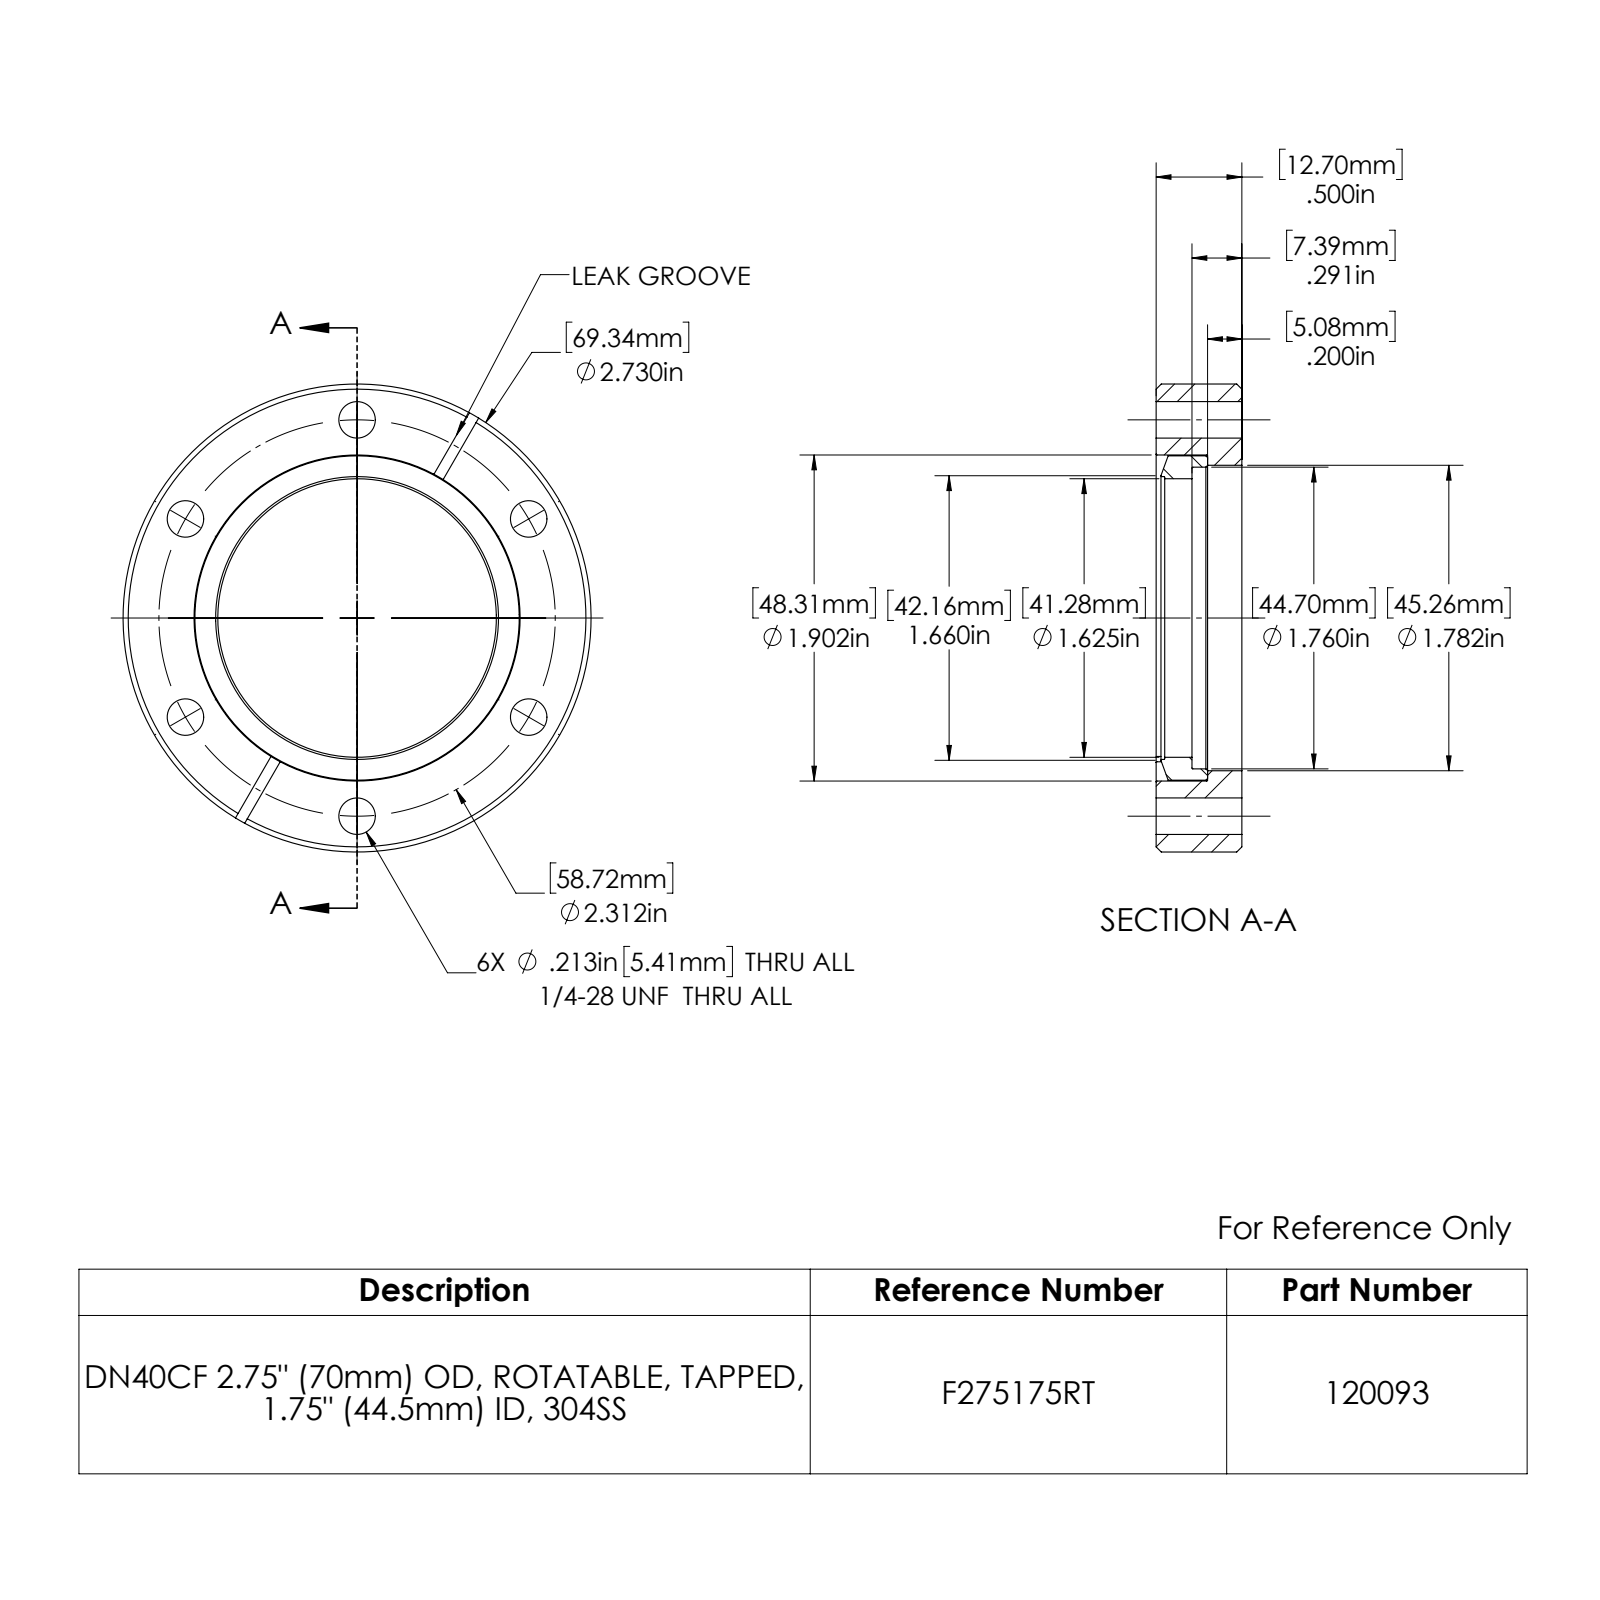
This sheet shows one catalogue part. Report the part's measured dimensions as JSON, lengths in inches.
{"part_name": "990367; 990365; 120093_A", "step_written_by": "SolidWorks 2022 (CONFIG_CONTROL_DESIGN)", "units": "inches", "bodies": {"solids": 2, "faces": 61, "planar": 13, "cylindrical": 26, "other": 22}, "overall_size": [2.73, 2.73, 0.5], "volume_in3": 1.61, "surface_area_in2": 19.47, "round_holes": [[0.213, 6], [1.625, 1], [1.65, 1], [1.76, 1], [1.782, 1], [1.902, 1]], "round_bosses_or_shafts": [[2.73, 1], [1.892, 1]], "face_to_face_distances": [0.5, 0.3, 0.2, 0.209, 0.091, 0.291, 0.062, 0.147, 0.238, 0.438], "hole_center_spacings": [1.156, 2.002, 1.156, 1.156, 2.002, 2.312, 2.312]}
